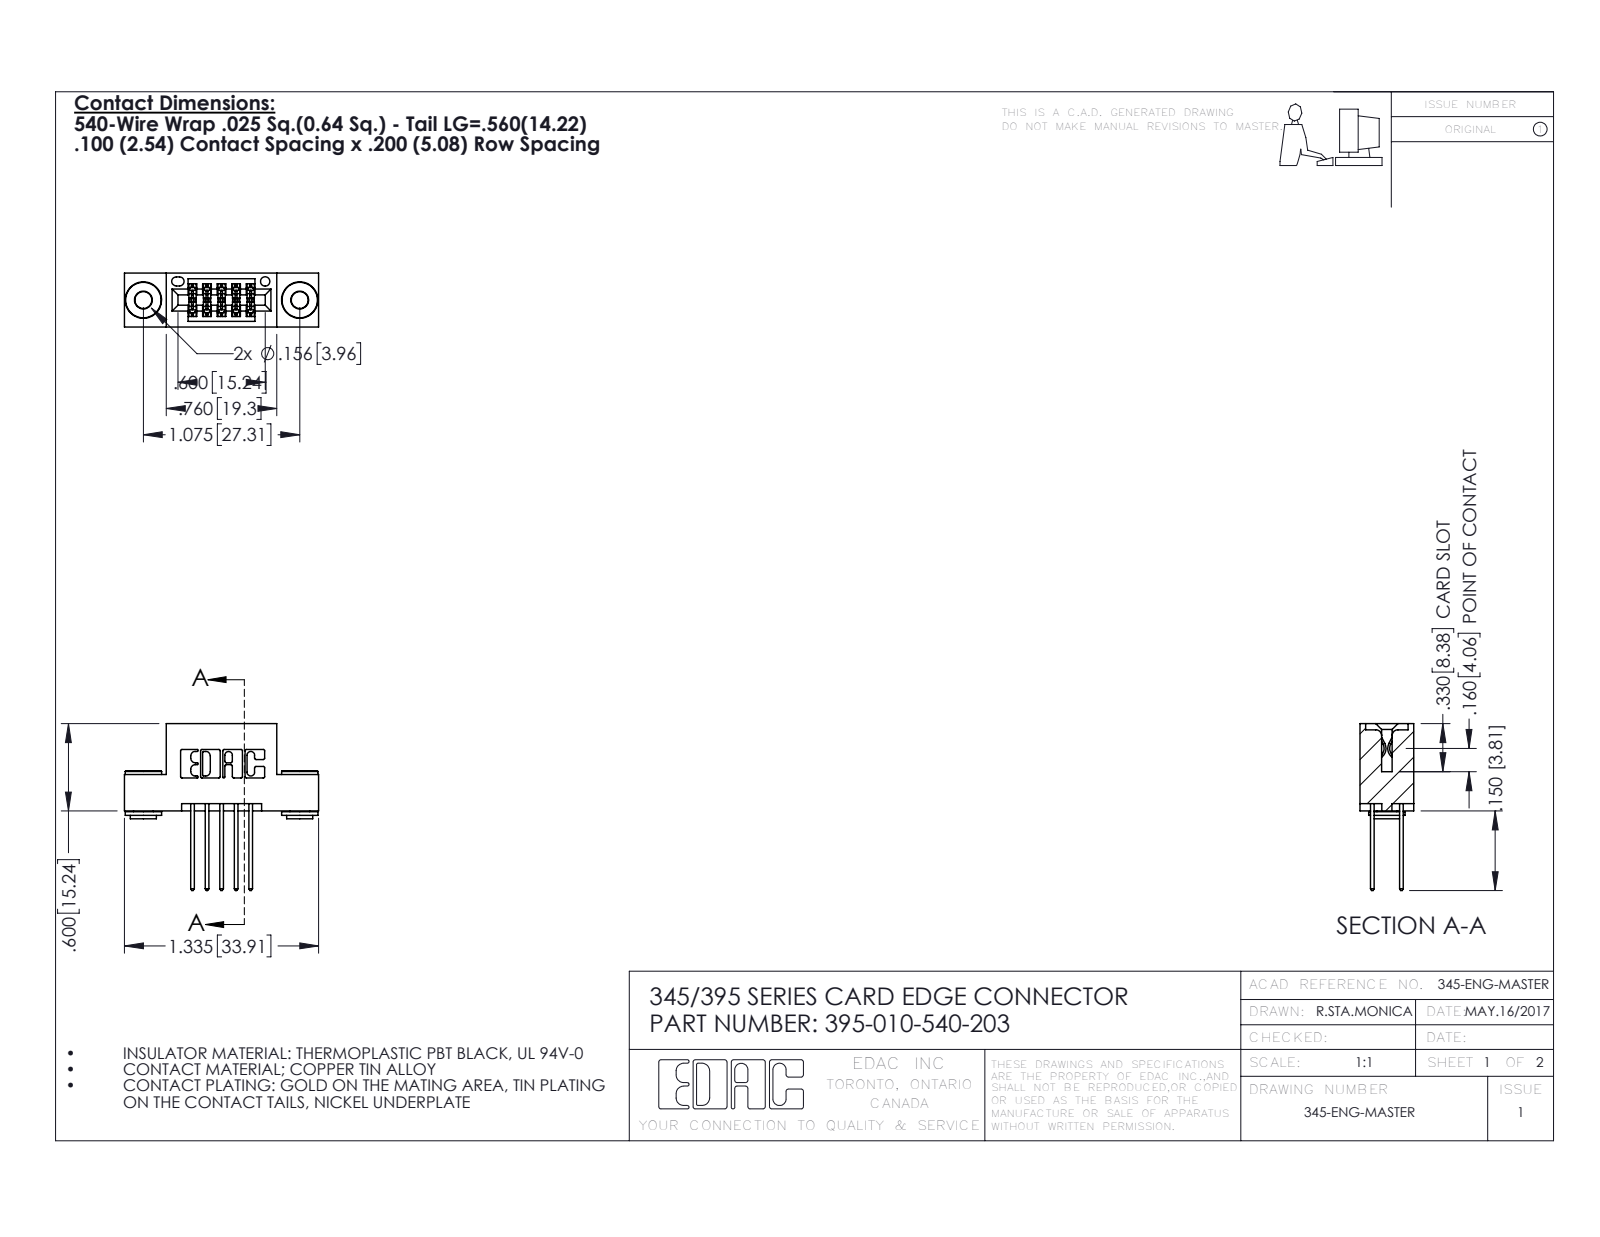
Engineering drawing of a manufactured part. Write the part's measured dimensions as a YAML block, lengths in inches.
part_name: "395-010-540-203; 345 Part_Flush Mounting Lugs - 0.156 Dia-TH; 345-292-001_345-293-140; 345-250-002_345-250-002-102"
step_written_by: "SolidWorks 2016 (CONFIG_CONTROL_DESIGN)"
units: inches
bodies: {solids: 13, faces: 664, planar: 420, cylindrical: 236, other: 8}
overall_size: [1.335, 1.147, 0.37]
volume: 0.184
surface_area: 6.371
round_holes:
  - {diameter: 0.116, count: 2}
  - {diameter: 0.156, count: 2}
  - {diameter: 0.064, count: 1}
round_bosses_or_shafts:
  - {diameter: 0.25, count: 2}
  - {diameter: 0.18, count: 2}
  - {diameter: 0.136, count: 2}
partial_cylinders:
  - {radius: 0.01, count: 22}
  - {radius: 0.006, count: 15}
  - {radius: 0.01, count: 10}
  - {radius: 0.007, count: 6}
  - {radius: 0.031, count: 6}
  - {radius: 0.026, count: 3}
  - {radius: 0.014, count: 2}
  - {radius: 0.019, count: 2}
face_to_face_distances: [0.2, 0.072, 0.298, 0.37, 0.1, 0.025, 0.098, 0.272, 0.225, 0.25]
hole_center_spacings: [0.27, 0.847, 1.075]
